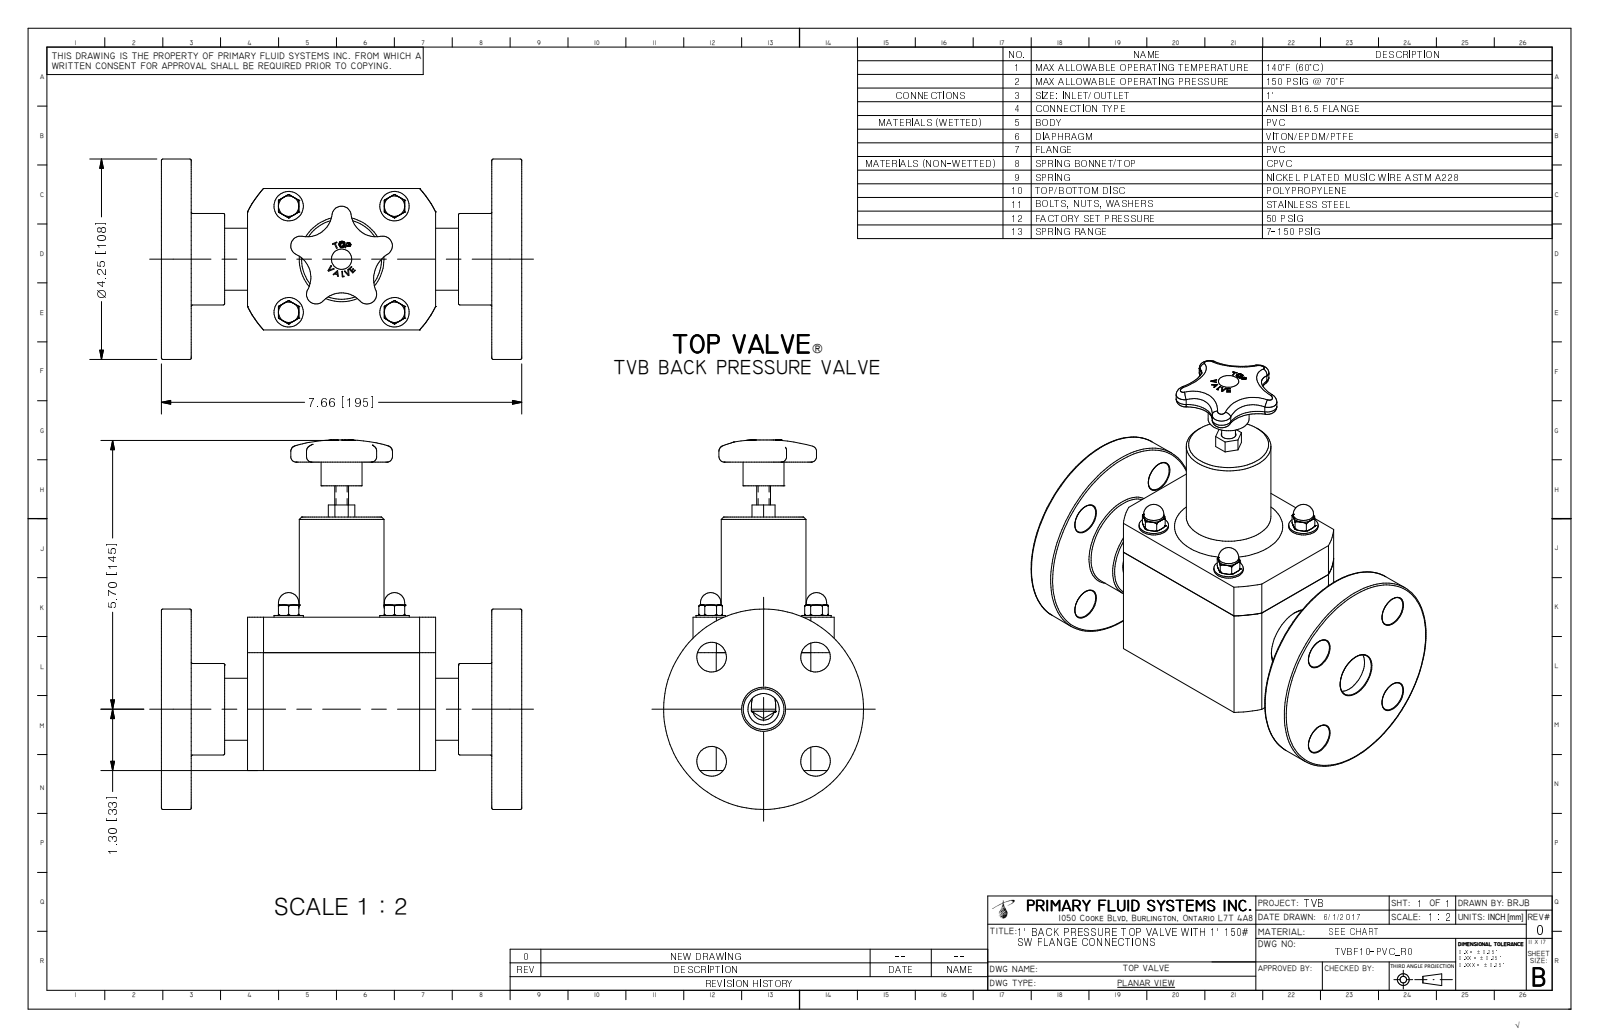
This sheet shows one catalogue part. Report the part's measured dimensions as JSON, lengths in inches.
{"part_name": "TVBF10-PVC_R0", "step_written_by": "Autodesk Inventor 2009 (AUTOMOTIVE_DESIGN)", "units": "inches", "bodies": {"solids": 1, "faces": 401, "planar": 156, "cylindrical": 65, "other": 180}, "overall_size": [7.837, 7.66, 4.25], "volume_in3": 62.79, "surface_area_in2": 219.8, "round_holes": [[0.175, 4], [0.63, 4], [0.936, 1], [0.957, 1]], "round_bosses_or_shafts": [[0.625, 4], [0.433, 4], [0.375, 4], [4.25, 1], [1.941, 1], [1.8, 1], [1.315, 1], [0.87, 1]], "partial_cylinders_radius": [[0.085, 5], [0.205, 5], [0.536, 4], [0.656, 4], [0.625, 1], [0.745, 1], [2.238, 1], [2.238, 1]], "face_to_face_distances": [0.635, 7.025, 7.66, 3, 1.83, 5.83, 1.195, 5.195, 6.39, 3.25], "hole_center_spacings": [1.562, 2.209, 2.25, 3.125, 3.182]}
